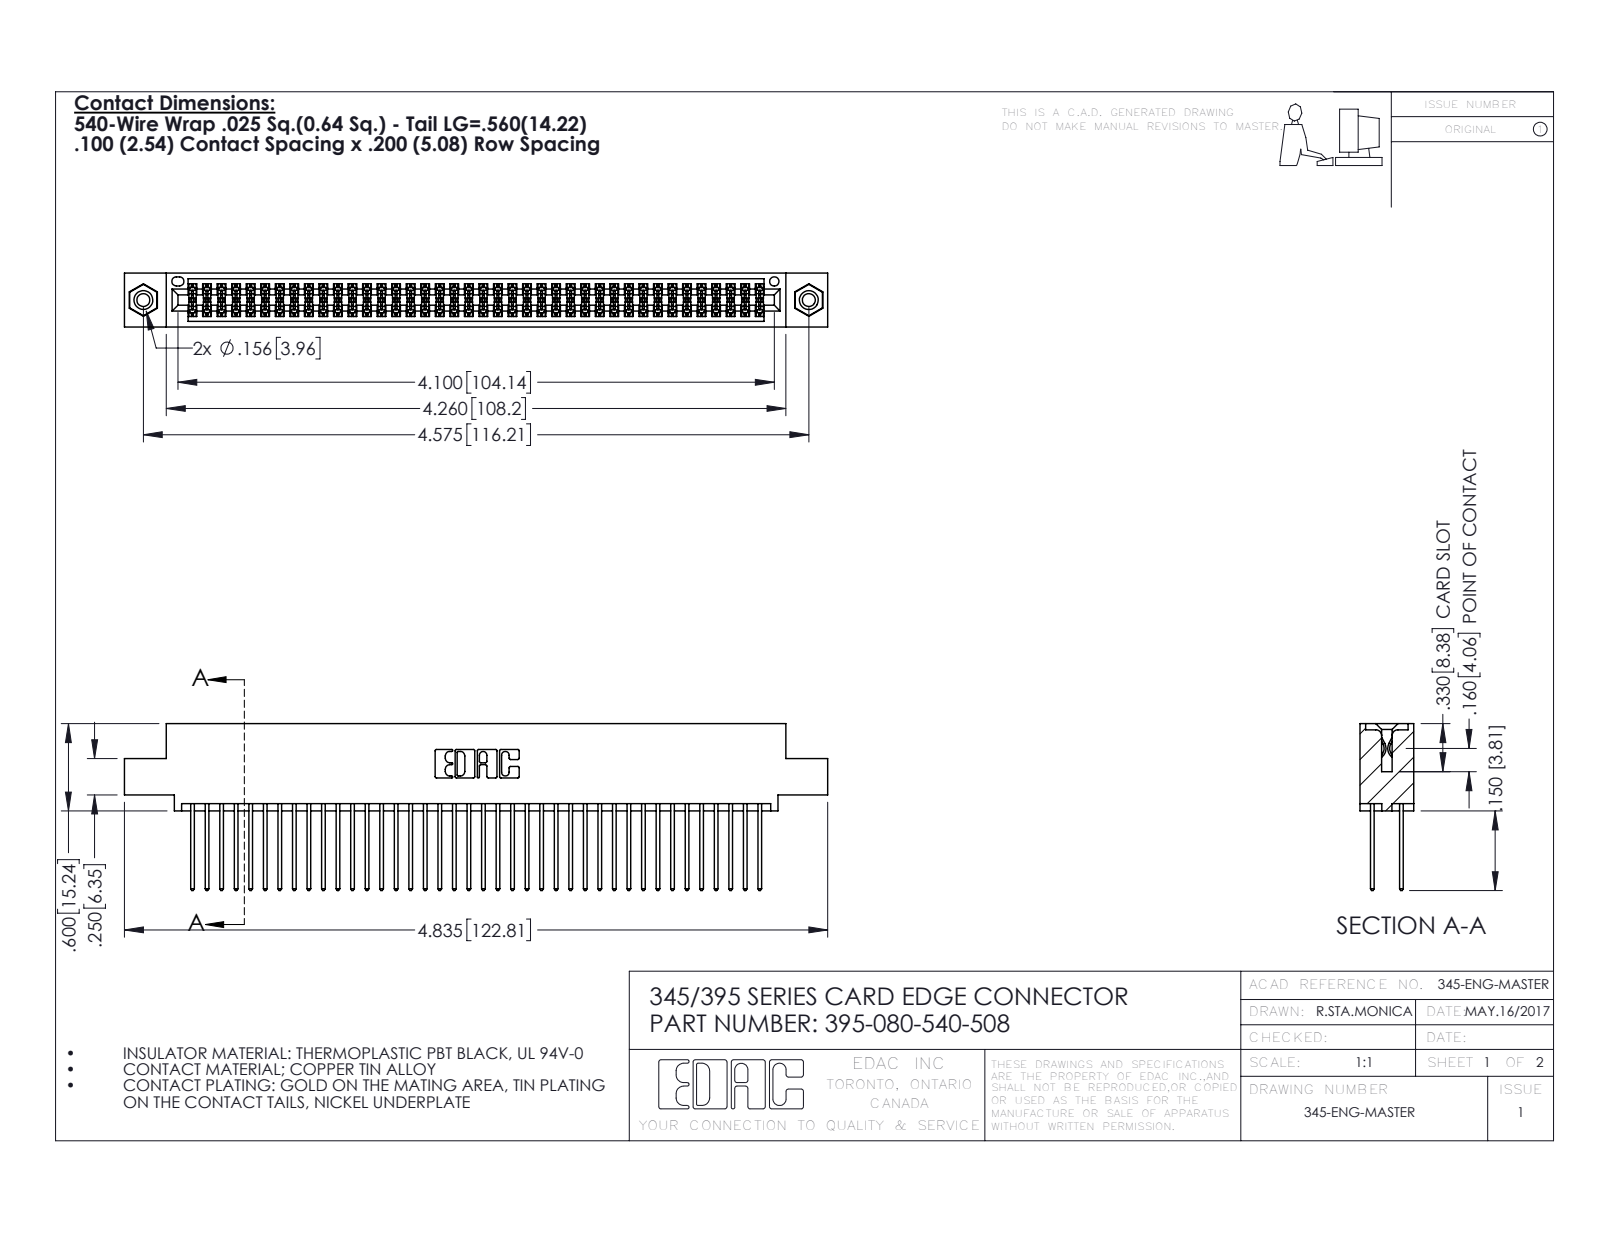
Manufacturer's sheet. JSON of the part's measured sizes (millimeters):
{"part_name": "395-080-540-508; 345-292-001_345-293-140; 345 Part_0.110 Offset - 0.156 Dia-TI; 345-250-001_345-250-003-102", "step_written_by": "SolidWorks 2016 (CONFIG_CONTROL_DESIGN)", "units": "millimeters", "bodies": {"solids": 83, "faces": 4190, "planar": 2756, "cylindrical": 1418, "other": 16}, "overall_size": [122.8, 29.1, 9.4], "volume_mm3": 12100, "surface_area_mm2": 19410, "round_holes": [[2.3, 2], [3.2, 2], [4, 2], [1.6, 1]], "round_bosses_or_shafts": [[3.9, 2]], "partial_cylinders_radius": [[0.2, 120], [0.3, 80], [0.3, 22], [0.2, 6], [0.8, 6], [0.7, 3], [0.4, 2], [0.5, 2]], "face_to_face_distances": [1.8, 7.6, 5.1, 2.5, 6.9, 0.6, 9.4, 5.7, 4.4, 3.8], "hole_center_spacings": [6.9, 110.2, 116.2]}
